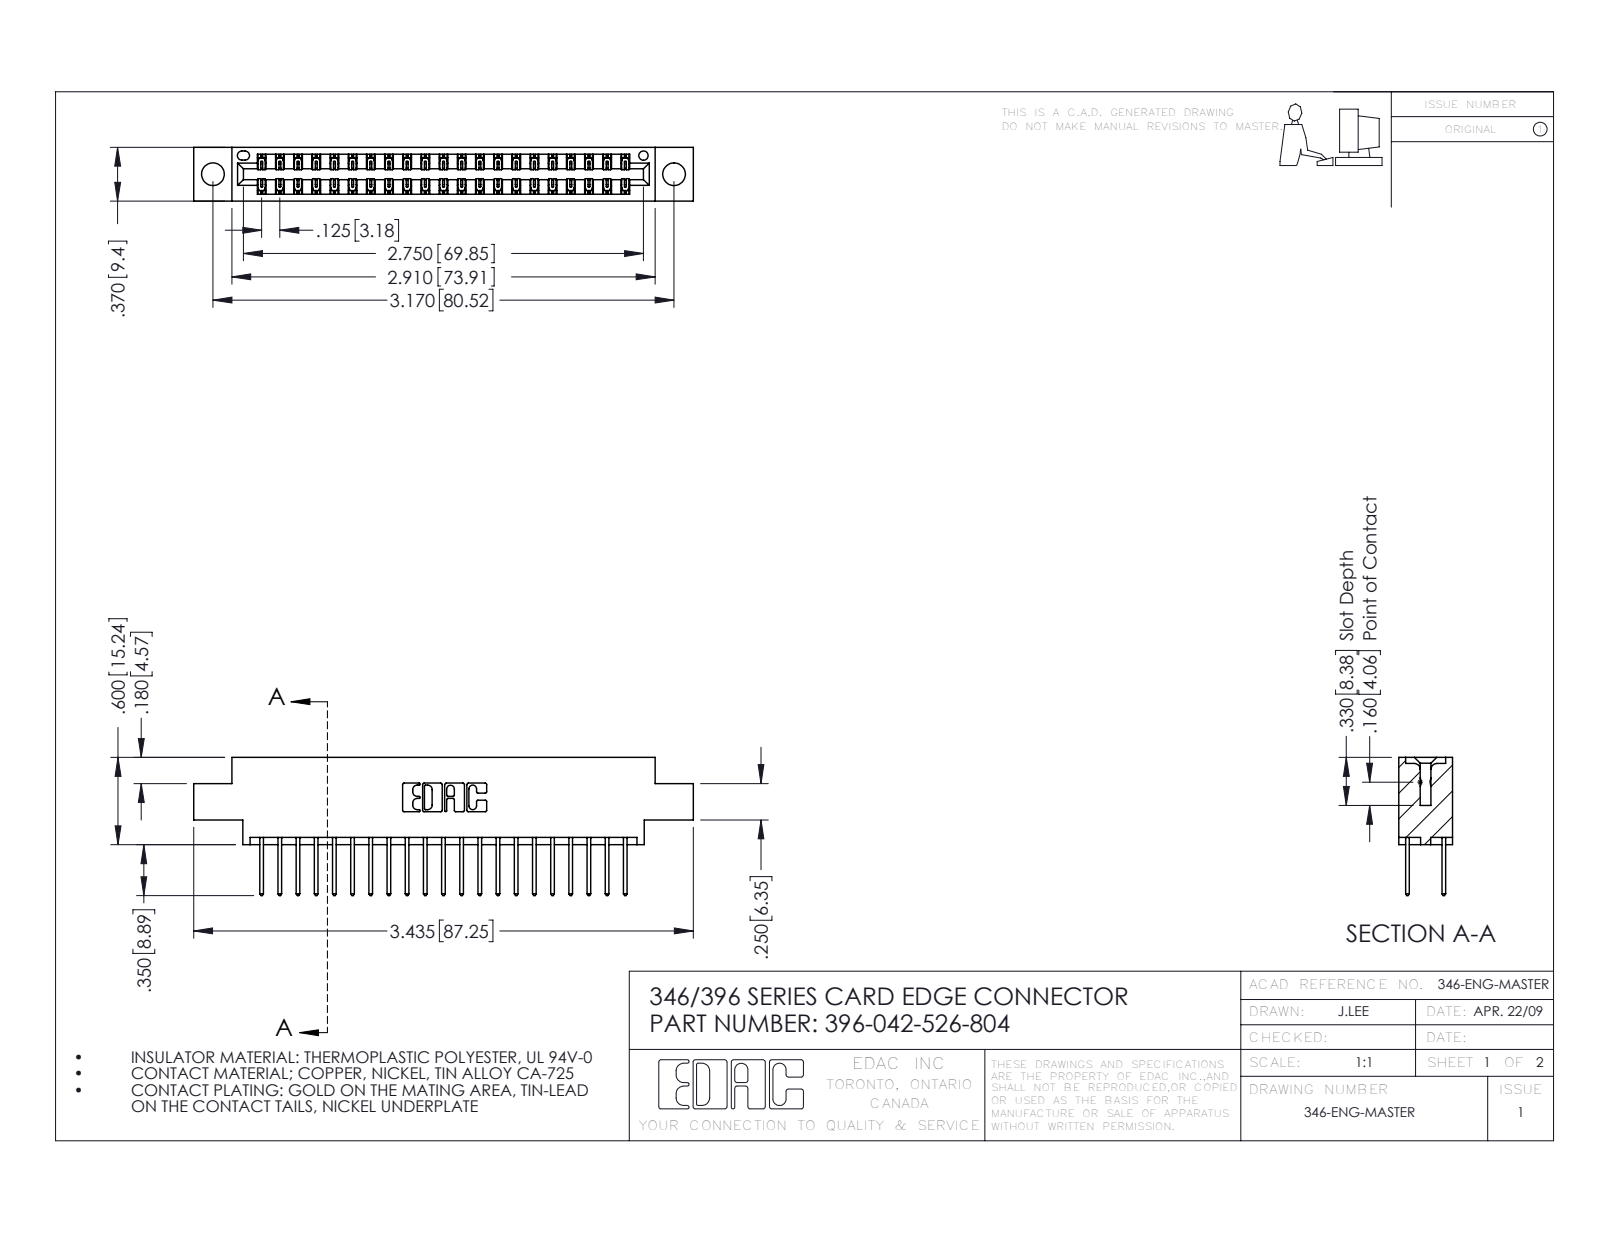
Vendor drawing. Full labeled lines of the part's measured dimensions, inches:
Part name (STEP PRODUCT): 346 Part_0.170 Offset - 0.156 Dia-TH; 345-292-001_345-293-126; 396-042-526-804
STEP written by: SolidWorks 2016 (CONFIG_CONTROL_DESIGN)
Units: inches
Bodies: 43 solids, 2310 faces (1550 planar, 760 cylindrical, 0 other)
Overall size (bounding box): 3.435 × 0.95 × 0.37
Volume: 0.499 in³ · Surface area: 17.36 in²
Round holes (diameter × count): ⌀0.156 ×2, ⌀0.064 ×1
Partial cylindrical surfaces — rounded edges, fillets, slot ends (radius × count): R0.006 ×63, R0.01 ×42, R0.01 ×22, R0.007 ×6, R0.031 ×6, R0.026 ×3, R0.014 ×2, R0.022 ×2
Main face-to-face distances: 0.048, 0.322, 0.25, 0.37, 0.072, 0.298, 0.025, 0.275, 0.148, 0.222
Hole centre spacings: 0.246, 2.963, 3.17
